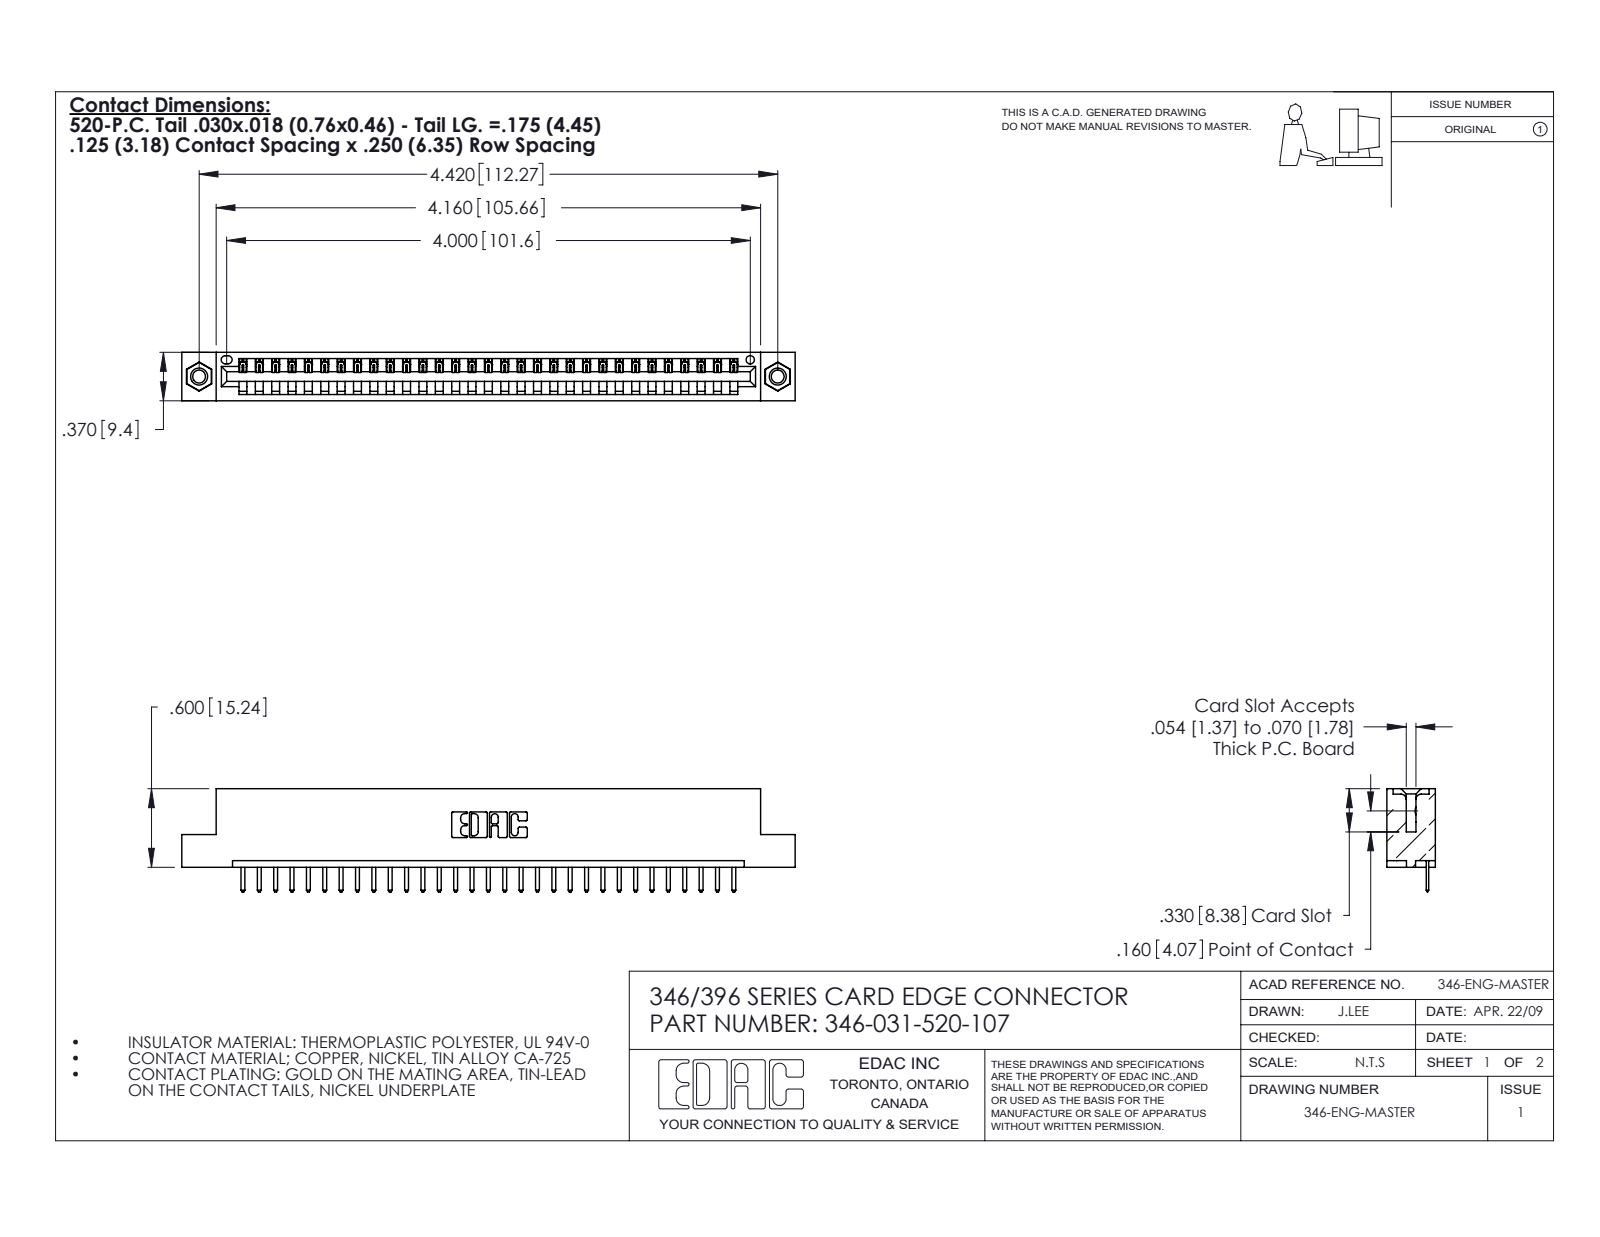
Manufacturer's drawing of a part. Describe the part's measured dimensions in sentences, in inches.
The part is named "346 Part_Flush Mounting Lugs - 0.156 Dia-TI; 345-250-001_345-250-005-103; 346-031-520-107; 345-292-001_345-293-120". Its 3-D file was written by "SolidWorks 2020 (CONFIG_CONTROL_DESIGN)". It is 34 solids with 2104 faces: 1410 planar, 678 cylindrical and 16 other. Overall it measures 4.685 by 0.788 by 0.37 inches. Its volume is 0.684 cubic inches and its surface area 21.13 square inches. Round holes: 2 of diameter 0.098, 2 of diameter 0.125, 2 of diameter 0.156, 1 of diameter 0.064. Round bosses or shafts: 2 of diameter 0.155. Partial cylindrical surfaces (rounded edges, fillets, slot ends): 64 of radius 0.01, 62 of radius 0.006, 22 of radius 0.01, 6 of radius 0.007, 6 of radius 0.031, 3 of radius 0.026, 2 of radius 0.031, 2 of radius 0.04. The main face-to-face distances are 0.048, 0.322, 0.37, 0.25, 0.148, 0.222, 0.1, 0.174, 0.072, 0.298. The hole center spacings are 0.246, 4.212, 4.42.
